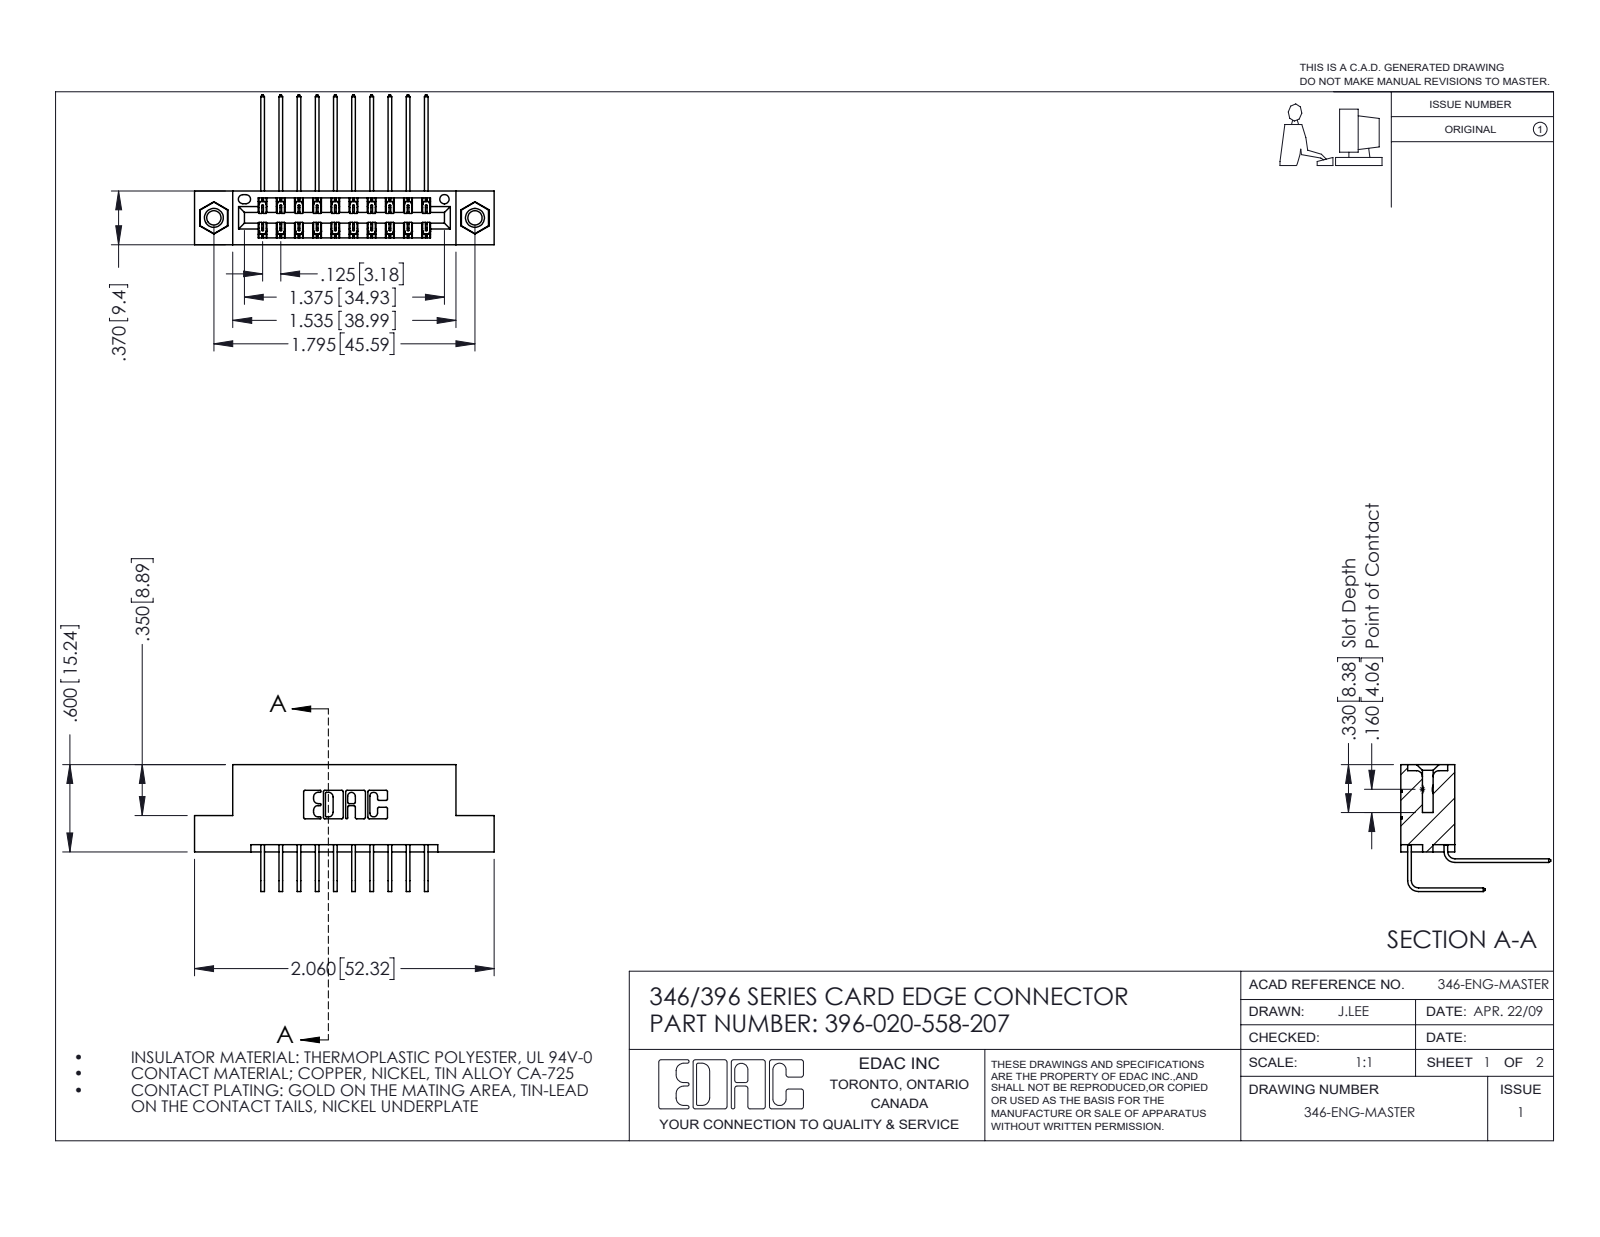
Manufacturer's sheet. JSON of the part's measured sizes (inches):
{"part_name": "345-250-001_345-250-005-103; 345-292-001_558 559 Tail - 1; 345-292-001_558 Tail - 2; 396-020-558-207 (+1 more)", "step_written_by": "SolidWorks 2016 (CONFIG_CONTROL_DESIGN)", "units": "inches", "bodies": {"solids": 23, "faces": 1262, "planar": 848, "cylindrical": 398, "other": 16}, "overall_size": [2.06, 1.03, 0.873], "volume_in3": 0.302, "surface_area_in2": 10.69, "round_holes": [[0.098, 2], [0.125, 2], [0.156, 2], [0.064, 1]], "round_bosses_or_shafts": [[0.155, 2]], "partial_cylinders_radius": [[0.006, 30], [0.01, 22], [0.007, 6], [0.031, 6], [0.026, 3], [0.014, 2], [0.022, 2], [0.024, 2]], "face_to_face_distances": [0.25, 0.322, 0.048, 0.37, 0.025, 0.298, 0.072, 0.275, 0.148, 0.222], "hole_center_spacings": [0.246, 1.59, 1.795]}
